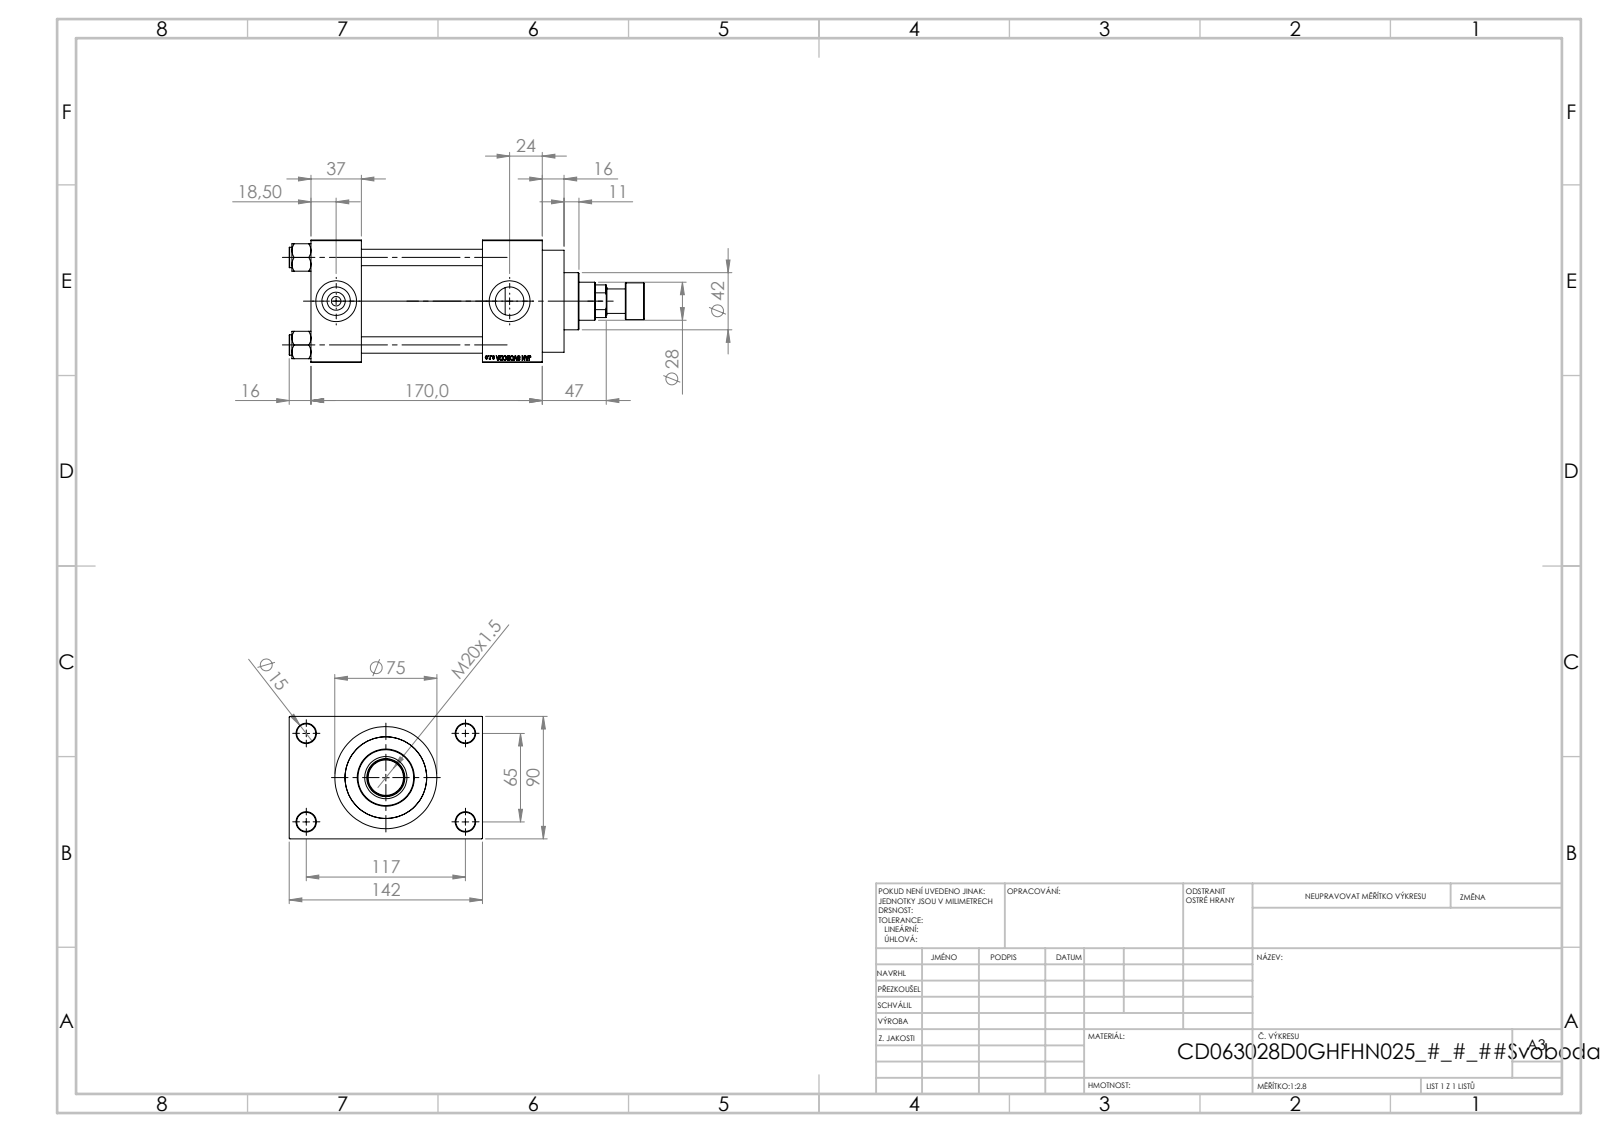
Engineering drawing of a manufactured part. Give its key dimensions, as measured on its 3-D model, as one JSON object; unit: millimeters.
{"part_name": "V215CD_D_TYCINKA; V215CD_VC_A; V215CD_NUT_M5_D; V215CD_VCP_D (+2 more)", "step_written_by": "SolidWorks 2019 (CONFIG_CONTROL_DESIGN)", "units": "millimeters", "bodies": {"solids": 12, "faces": 1117, "planar": 501, "cylindrical": 92, "other": 524}, "overall_size": [261, 142, 90], "volume_mm3": 1159000, "surface_area_mm2": 223174, "round_holes": [[12, 4], [14, 4], [7, 2], [20.96, 2], [30, 2], [18.5, 1], [28, 1], [31, 1], [50, 1], [60, 1], [63, 1]], "round_bosses_or_shafts": [[15, 4], [75, 1], [69, 1], [42, 1], [27, 1], [18, 1]], "face_to_face_distances": [90, 89, 37, 126, 133, 170, 44, 26, 116, 142], "hole_center_spacings": [26.35, 45.47, 64.3, 66.92, 69.81, 90.65, 111.34, 65]}
